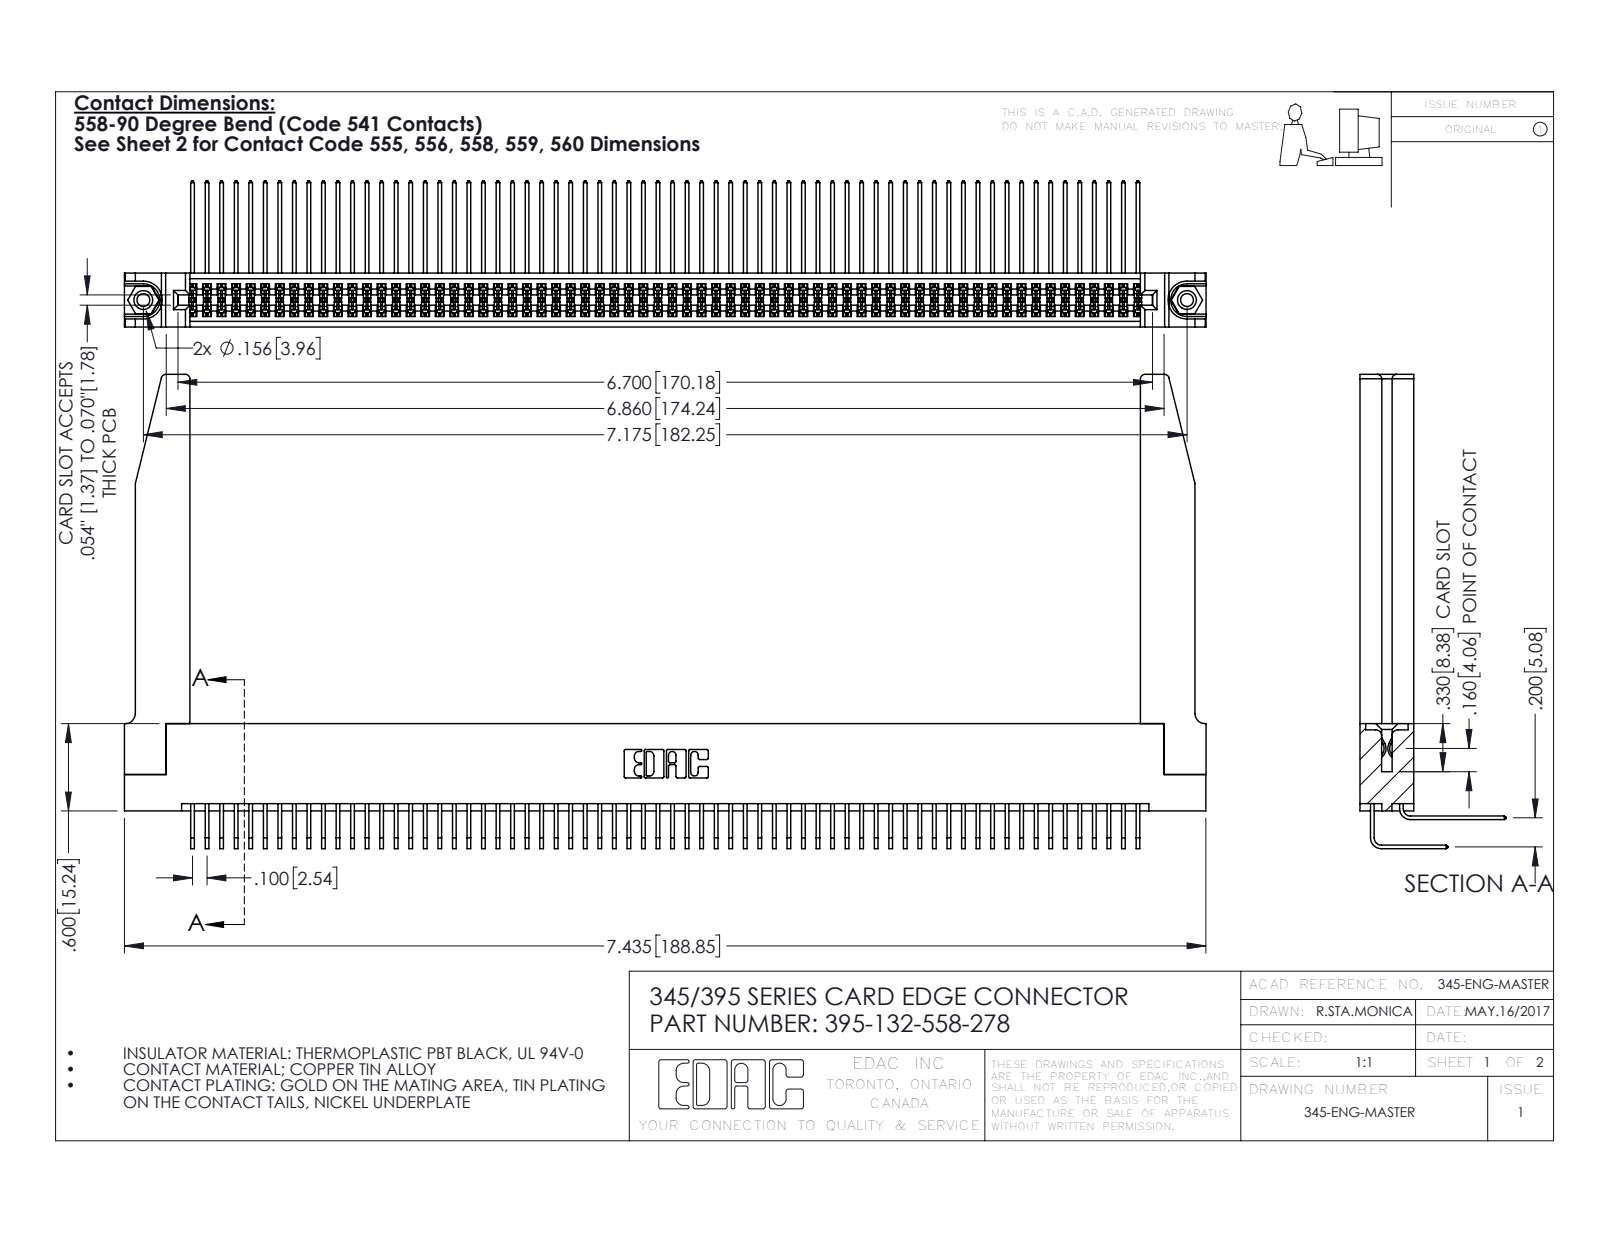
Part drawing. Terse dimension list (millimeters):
name: 345 Part_Flush Mounting Lugs - 0.156 Dia-TH; 345-250-001_345-250-001-102; 345-292-001_558 Tail - 2; 395-132-558-278 (+2 more)
written by: SolidWorks 2016 (CONFIG_CONTROL_DESIGN)
unit: mm
bodies: 137 solids, 7224 faces (4842 planar, 2330 cylindrical, 52 other)
size: 188.9 × 82.8 × 25.5
volume: 27 100 mm³; area: 39 460 mm²
holes: 2× ⌀2.3, 2× ⌀3.2, 2× ⌀4, 1× ⌀1.6
bosses: 2× ⌀3.9
rounds: 199× R0.2, 22× R0.3, 8× R0.8, 6× R0.2, 6× R0.8, 3× R0.7, 2× R0.4, 2× R0.5
face distances: 1.8, 7.6, 9.4, 5.1, 2.5, 6.9, 0.6, 5.7, 0.6, 7.2
hole spacings: 6.9, 176.3, 182.2
